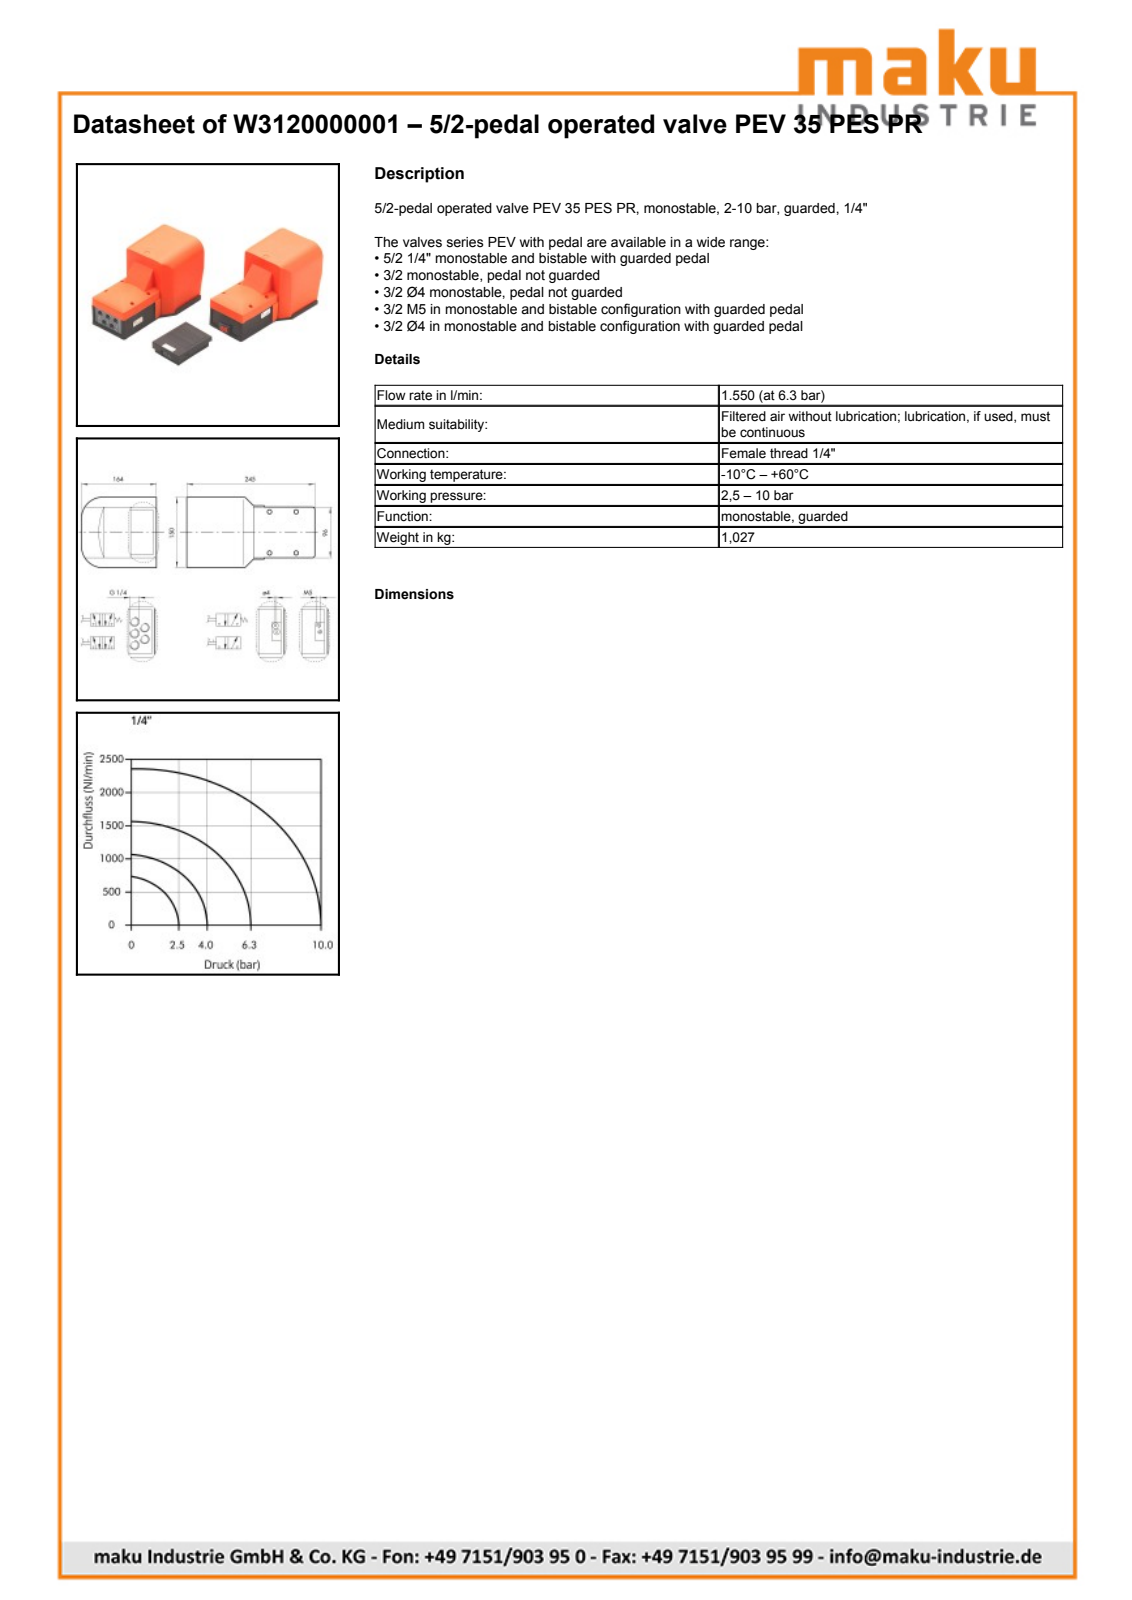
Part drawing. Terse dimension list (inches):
name: W3120000001(3SPR); W3120000001Pedal; W3120000001Body; W3120000001Body1 (+2 more)
written by: PARTsolutions (AUTOMOTIVE_DESIGN)
unit: in
bodies: 8 solids, 465 faces (356 planar, 78 cylindrical, 31 other)
size: 9.547 × 6.457 × 5.906
volume: 38.1 in³; area: 489.8 in²
holes: 5× ⌀0.451, 4× ⌀0.157, 1× ⌀0.315, 1× ⌀1.102
bosses: 4× ⌀0.512, 4× ⌀0.354, 4× ⌀0.315, 4× ⌀0.276, 2× ⌀0.394, 1× ⌀1.417, 1× ⌀0.866, 1× ⌀0.165
rounds: 4× R0.157, 3× R0.236, 2× R0.059, 2× R0.886, 2× R0.984, 1× R0.3
face distances: 0.098, 0.276, 5.61, 4.646, 0.965, 4.744, 0.866, 1.063, 5.709, 4.547
hole spacings: 0.864, 0.874, 0.886, 1.516, 2.008, 3.15, 3.251, 3.735
